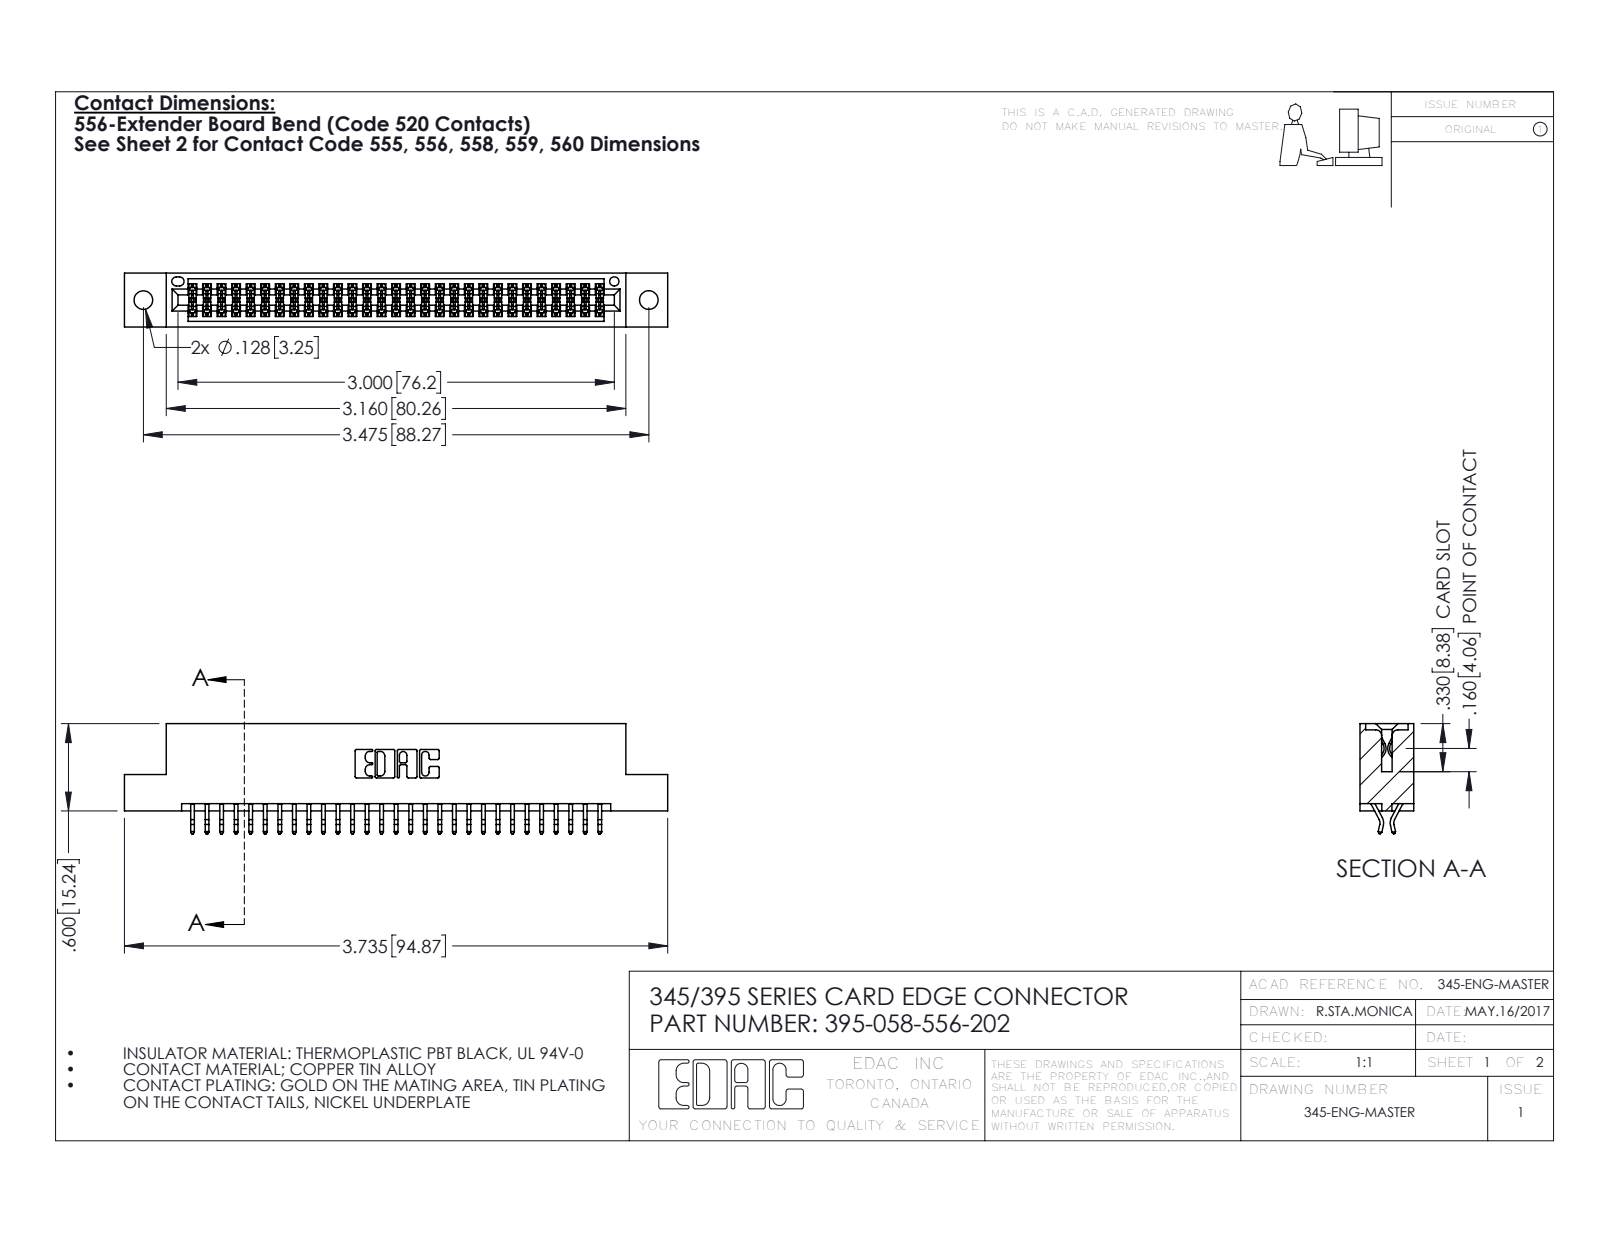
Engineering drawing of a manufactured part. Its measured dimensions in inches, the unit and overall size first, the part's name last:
Units: inches
Overall size (bounding box): 3.735 × 0.757 × 0.37
Round holes (diameter × count): ⌀0.128 ×2, ⌀0.064 ×1
Partial cylindrical surfaces — rounded edges, fillets, slot ends (radius × count): R0.006 ×87, R0.01 ×22, R0.007 ×6, R0.031 ×6, R0.026 ×3, R0.01 ×2, R0.014 ×2, R0.019 ×2
Main face-to-face distances: 0.298, 0.072, 0.2, 0.37, 0.025, 0.098, 0.272, 0.225, 0.175, 0.149
Hole centre spacings: 0.27, 3.24, 3.475
Volume: 0.553 in³ · Surface area: 19.86 in²
Bodies: 59 solids, 3374 faces (2226 planar, 1148 cylindrical, 0 other)
Part name (STEP PRODUCT): 345 Part_Flush Mounting Lugs - 0.128 Dia; 395-058-556-202; 345-292-001_556 Tail
STEP written by: SolidWorks 2016 (CONFIG_CONTROL_DESIGN)
